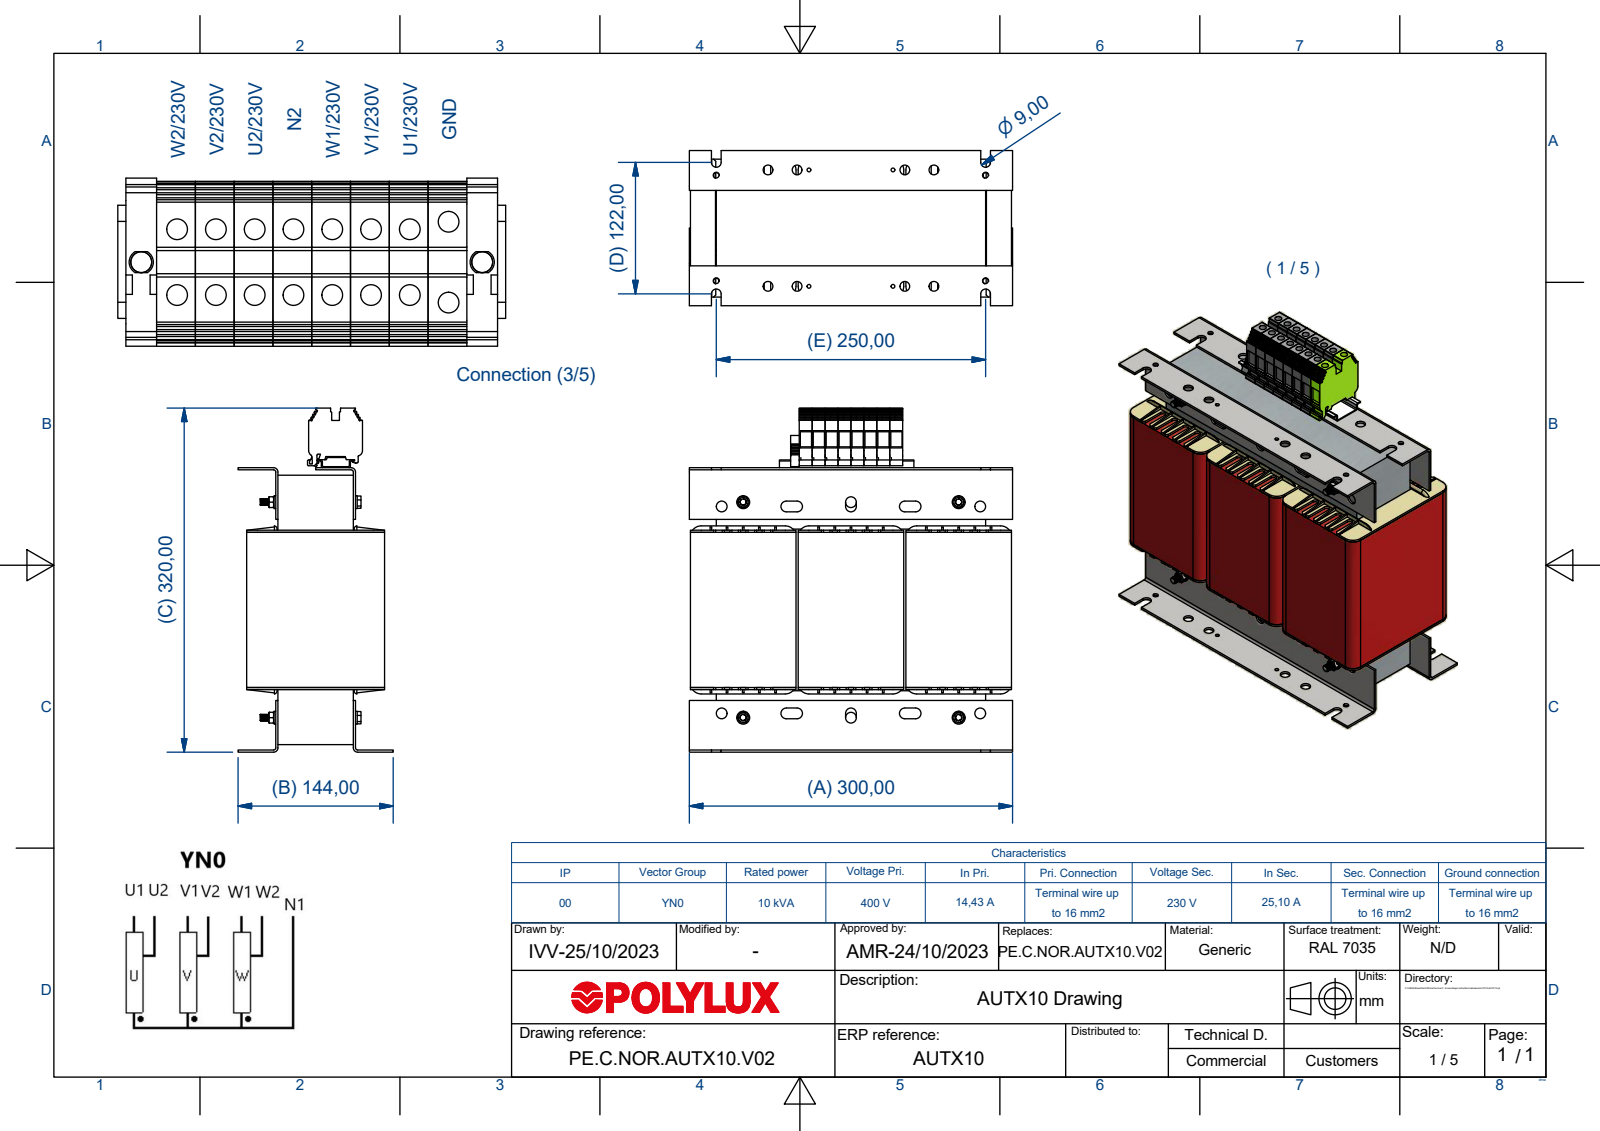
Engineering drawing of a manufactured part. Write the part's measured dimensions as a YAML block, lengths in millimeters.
part_name: "AUTX10"
step_written_by: "Autodesk Inventor 2018 (AUTOMOTIVE_DESIGN)"
units: millimeters
bodies: {solids: 0, faces: 2027, planar: 1476, cylindrical: 507, other: 44}
overall_size: [319.3, 300, 144]
round_holes:
  - {diameter: 6.4, count: 16}
  - {diameter: 9, count: 10}
  - {diameter: 4.92, count: 6}
  - {diameter: 10, count: 6}
  - {diameter: 3.5, count: 4}
  - {diameter: 5.8, count: 1}
round_bosses_or_shafts:
  - {diameter: 12, count: 4}
  - {diameter: 6, count: 4}
partial_cylinders:
  - {radius: 0.5, count: 49}
  - {radius: 3, count: 28}
  - {radius: 5, count: 12}
  - {radius: 10, count: 12}
  - {radius: 1, count: 11}
  - {radius: 2, count: 6}
  - {radius: 4.5, count: 6}
  - {radius: 0.2, count: 5}
face_to_face_distances: [2, 99, 58, 204, 70, 29, 100, 74, 101, 72]
hole_center_spacings: [12, 23.62, 48.26, 108, 202.06, 72, 11, 20.35]
